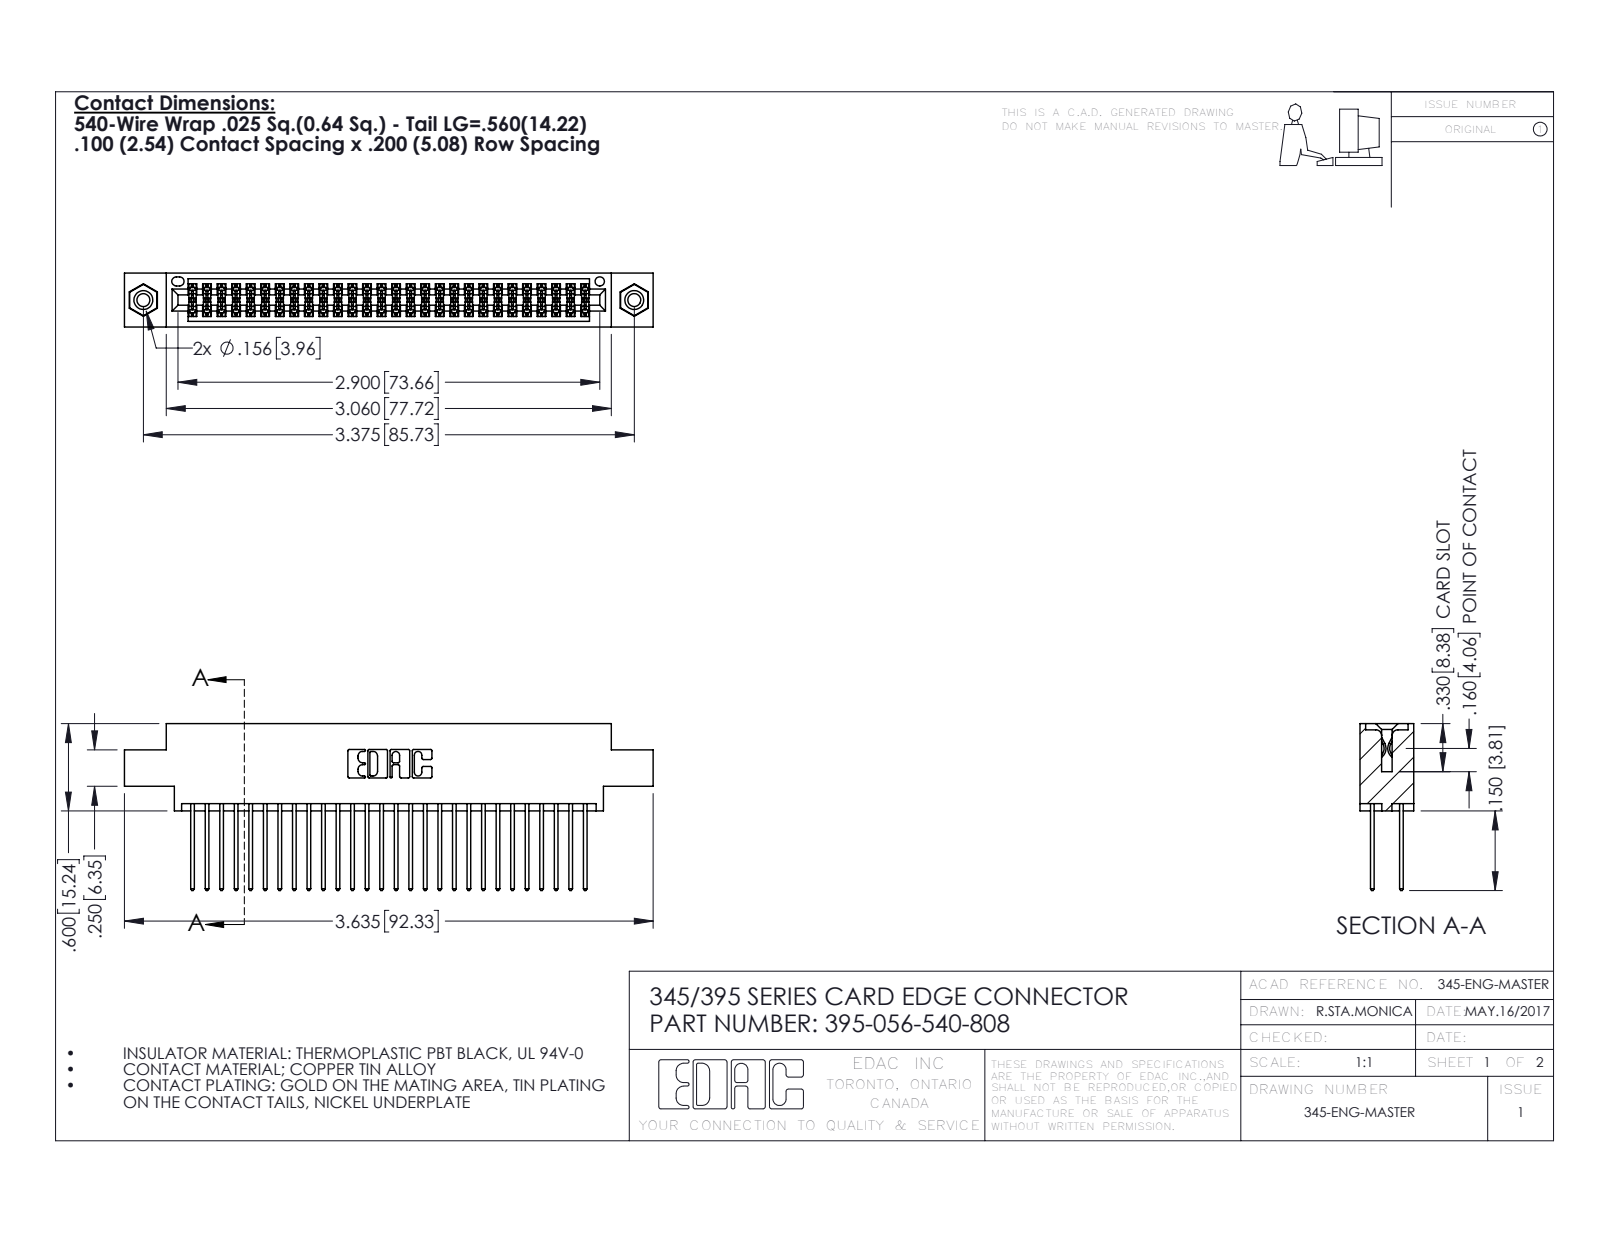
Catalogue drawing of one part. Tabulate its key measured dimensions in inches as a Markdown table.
| quantity | value |
| --- | --- |
| part name | 345 Part_0.170 Offset - 0.156 Dia-TI; 345-250-001_345-250-003-102; 345-292-001_345-293-140; 395-056-540-808 |
| STEP written by | SolidWorks 2016 (CONFIG_CONTROL_DESIGN) |
| units | inches |
| bodies | 59 solids, 2990 faces (1964 planar, 1010 cylindrical, 16 other) |
| overall size | 3.635 × 1.147 × 0.37 |
| volume | 0.545 in³ |
| surface area | 21.81 in² |
| round holes (diameter × count) | 0.089 × 2, 0.125 × 2, 0.156 × 2, 0.064 × 1 |
| round bosses / shafts (diameter × count) | 0.155 × 2 |
| partial cylindrical surfaces (radius × count) | 0.006 × 84, 0.01 × 56, 0.01 × 22, 0.007 × 6, 0.031 × 6, 0.026 × 3, 0.014 × 2, 0.019 × 2 |
| main face-to-face distances | 0.072, 0.298, 0.2, 0.098, 0.272, 0.025, 0.37, 0.225, 0.175, 0.149 |
| hole center spacings | 0.27, 3.14, 3.375 |
